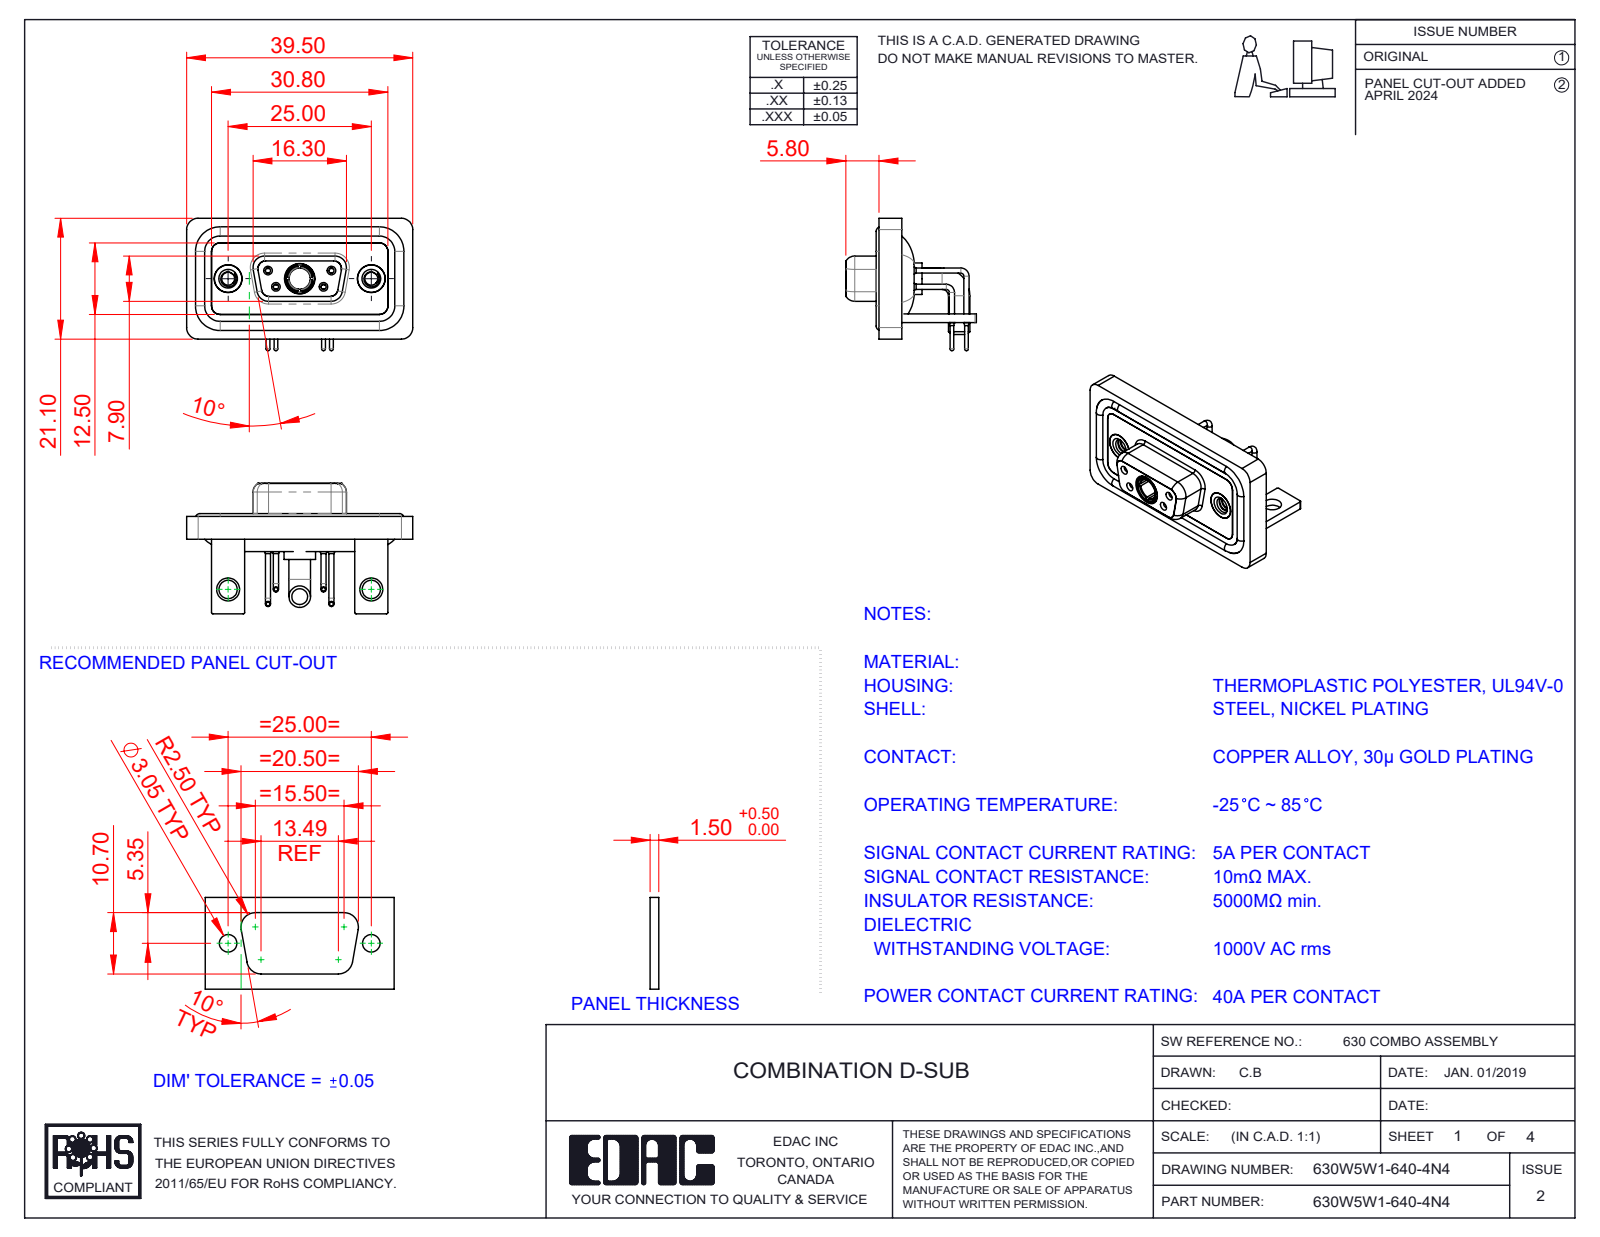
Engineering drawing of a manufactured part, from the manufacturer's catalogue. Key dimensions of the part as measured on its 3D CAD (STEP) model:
Part name (STEP PRODUCT): 630Combo Waterproof Housing_09 Contacts; 630Combo Stabilizer Bracket_50 Contacts; 630Combo Shell Rear_09 Contacts; 630Combo Shell Front_09 Contacts (+6 more)
STEP written by: SolidWorks 2023 (CONFIG_CONTROL_DESIGN)
Units: millimetres
Bodies: 15 solids, 724 faces (214 planar, 329 cylindrical, 181 other)
Overall size (bounding box): 39.5 × 23.12 × 22.8
Volume: 5 268 mm³ · Surface area: 8 622 mm²
Round holes (diameter × count): ⌀0.9 ×4, ⌀1.1 ×4, ⌀1.5 ×4, ⌀2 ×4, ⌀4.85 ×3, ⌀1.6 ×2, ⌀1.7 ×2, ⌀2.26 ×2, ⌀3.2 ×2, ⌀4 ×2, ⌀4.05 ×2, ⌀5 ×2
Round bosses / shafts (diameter × count): ⌀1.6 ×6, ⌀0.9 ×4, ⌀0.65 ×4, ⌀4.95 ×2, ⌀4.8 ×2, ⌀3.75 ×2, ⌀5.5 ×1, ⌀5.2 ×1
Partial cylindrical surfaces — rounded edges, fillets, slot ends (radius × count): R2 ×19, R1.5 ×18, R0.25 ×16, R1.35 ×8, R1.6 ×8, R0.5 ×5, R0.6 ×4, R0.65 ×4
Main face-to-face distances: 0.4, 2.9, 1.5, 1.8, 1.1, 3.7, 1.6, 0.8, 2.5, 3.1
Hole centre spacings: 3.16, 5.72, 7.1, 12.5, 18.1, 25, 4.39, 4.4
